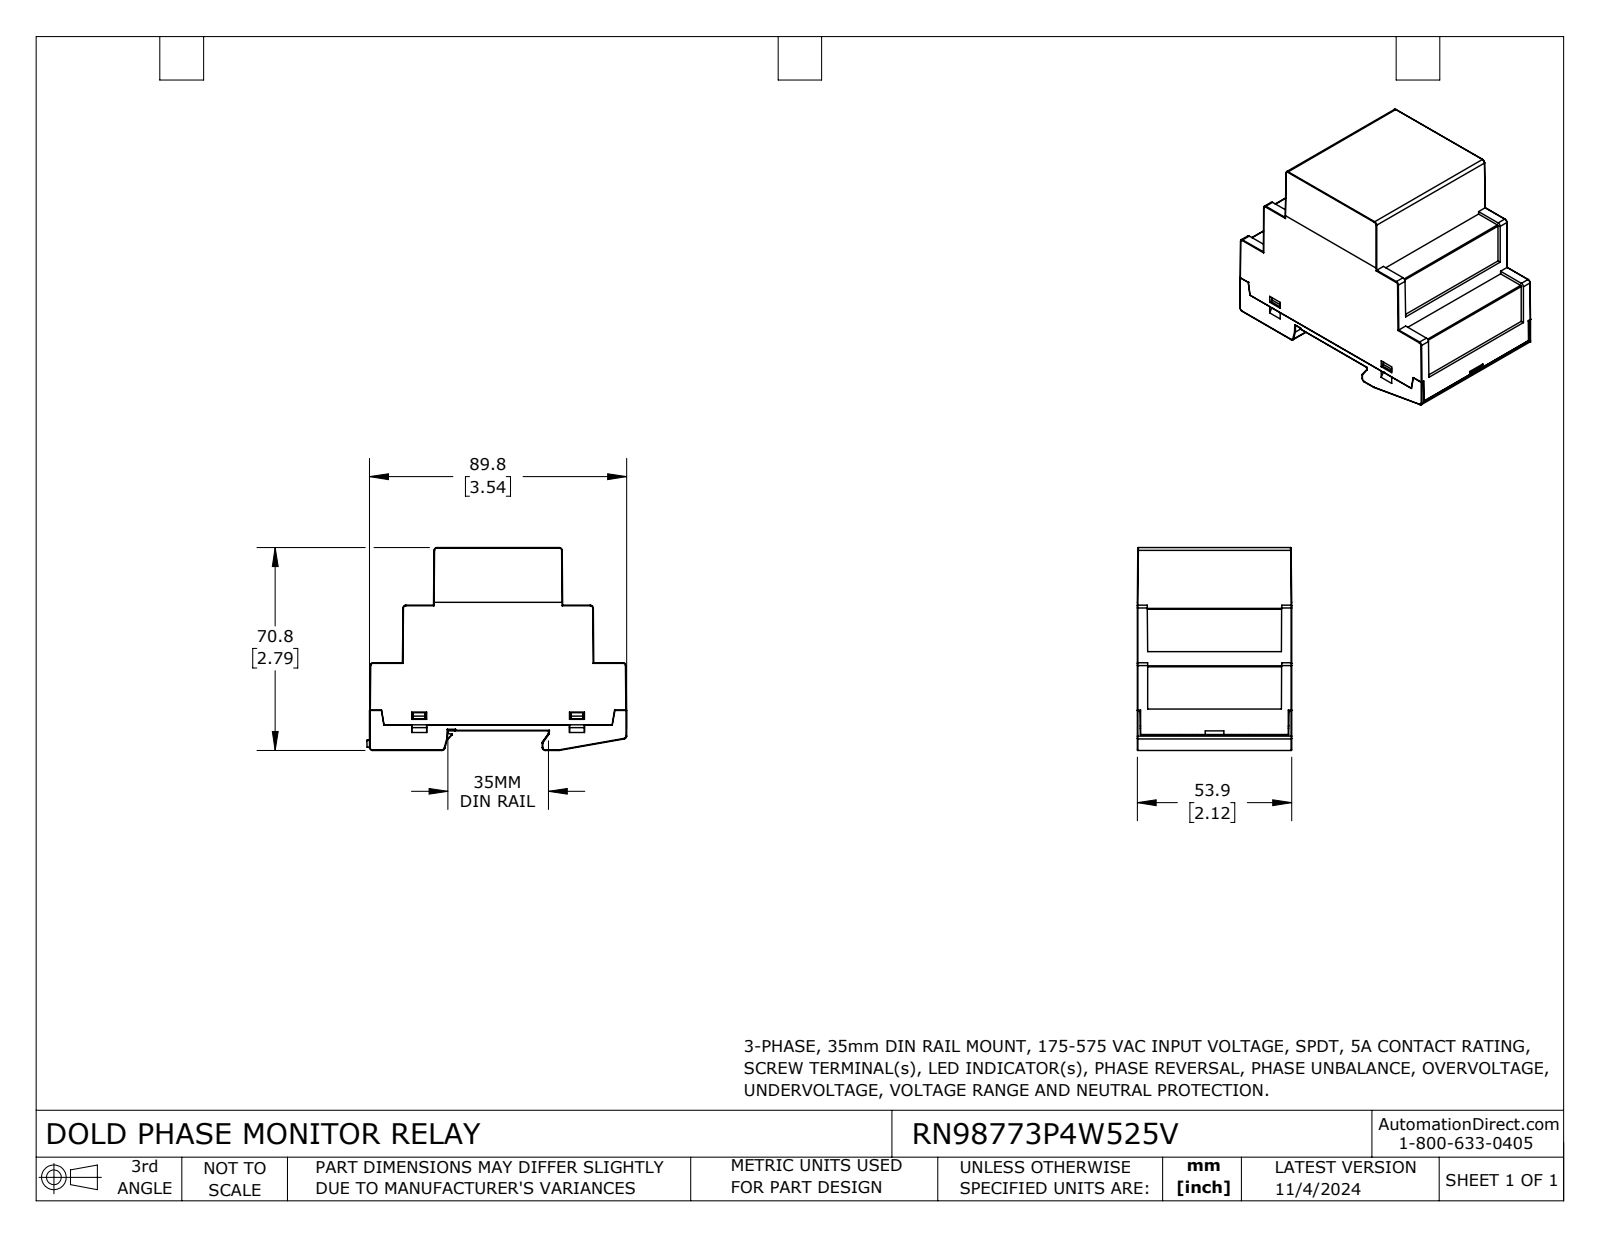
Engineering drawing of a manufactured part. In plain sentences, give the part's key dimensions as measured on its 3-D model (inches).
The part is named "RN98773P4W525V". Its 3-D file was written by "SolidWorks 2023 (CONFIG_CONTROL_DESIGN)". It is 3 solids with 1027 faces: 823 planar, 126 cylindrical and 78 other. Overall it measures 3.572 by 2.787 by 2.122 inches. Its volume is 13.92 cubic inches and its surface area 70.57 square inches. Round bosses or shafts: 5 of diameter 0.098, 1 of diameter 0.181. Partial cylindrical surfaces (rounded edges, fillets, slot ends): 44 of radius 0.008, 18 of radius 0.039, 11 of radius 0.02, 9 of radius 0.004, 4 of radius 0.012, 2 of radius 0.016, 1 of radius 0.011, 1 of radius 0.028. The main face-to-face distances are 2.122, 2.435, 0.041, 0.085, 2.52, 0.217, 0.352, 0.26, 0.175, 2.26.
